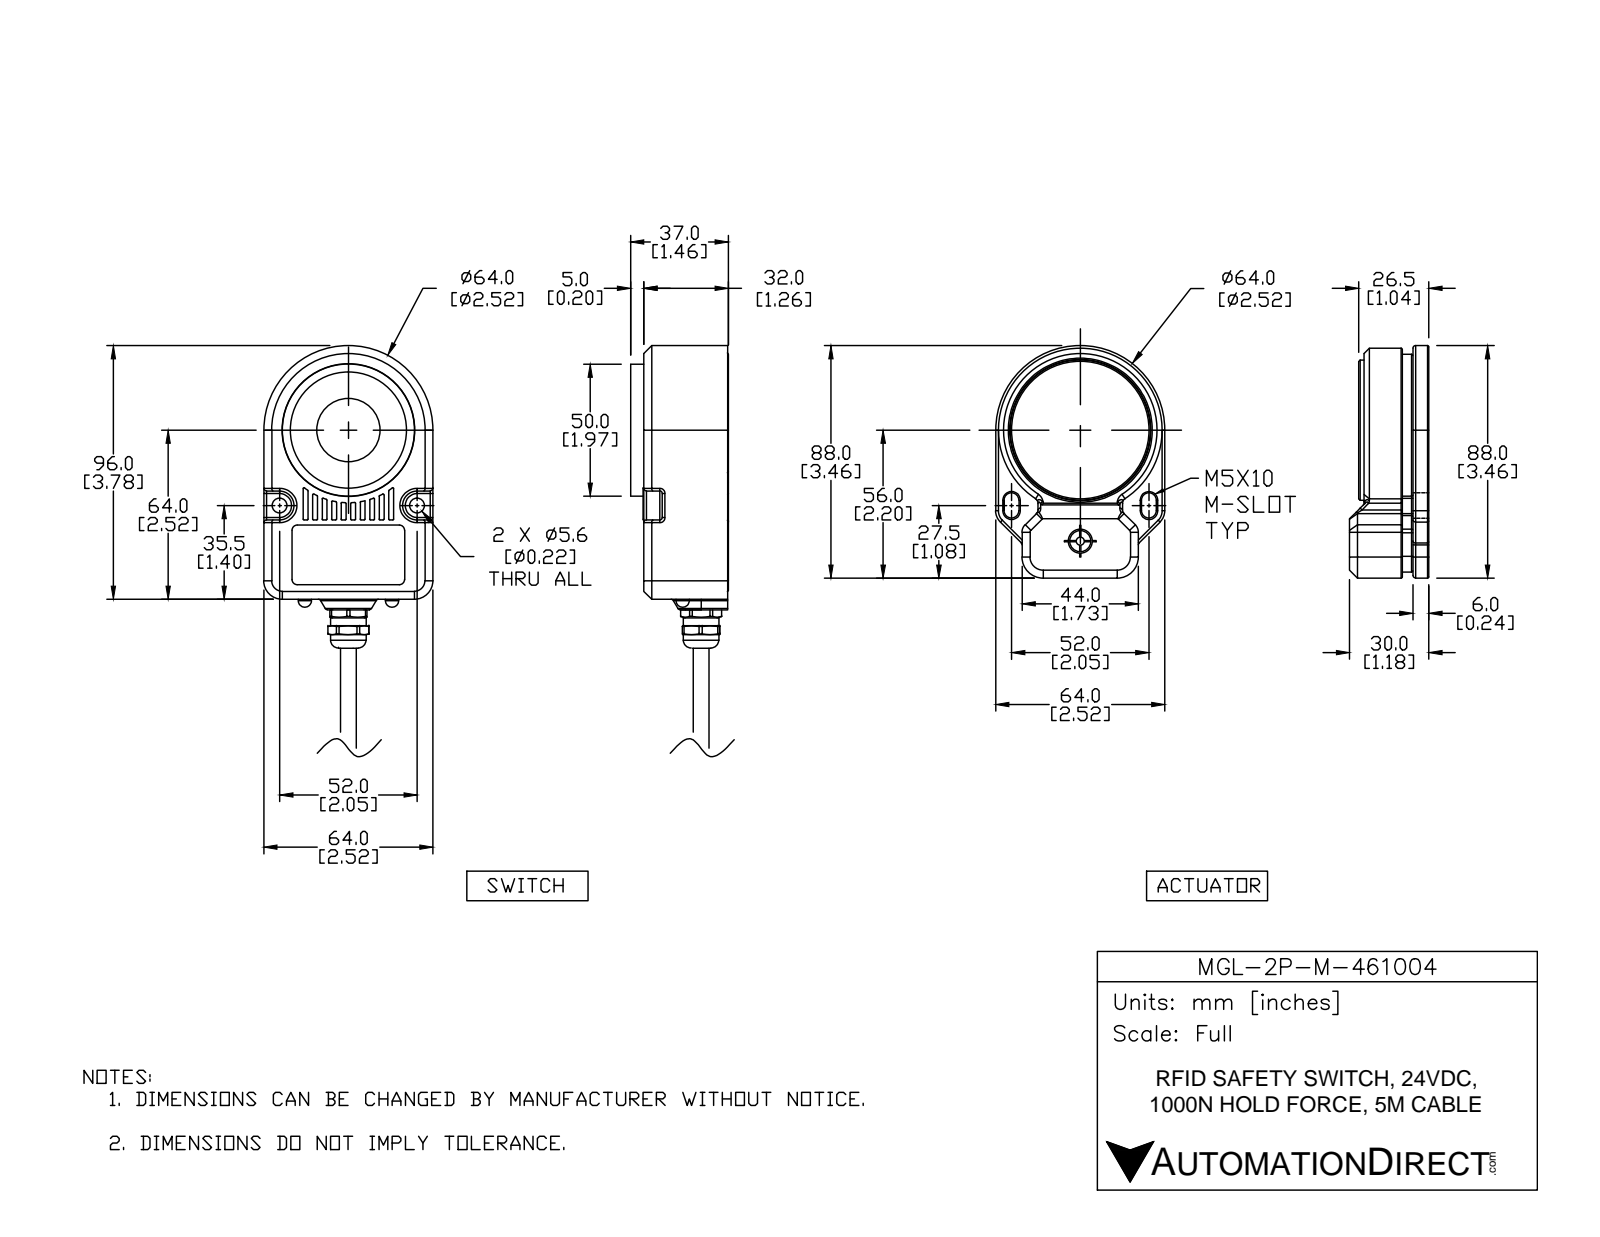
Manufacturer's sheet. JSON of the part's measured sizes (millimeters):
{"part_name": "MGL-2P-M-461004_2; MGL-2P-M-461004; MGL-2P-M-461004_1", "step_written_by": "SolidWorks 2017 (AUTOMOTIVE_DESIGN)", "units": "millimeters", "bodies": {"solids": 17, "faces": 1585, "planar": 431, "cylindrical": 674, "other": 480}, "overall_size": [196, 64.5, 64], "volume_mm3": 194400, "surface_area_mm2": 99680, "round_holes": [[4, 6], [8, 6], [2.4, 4], [5, 4], [2, 2], [3.3, 2], [5.6, 2], [9, 2], [10.5, 2], [17, 2], [6.4, 1], [6.5, 1]], "round_bosses_or_shafts": [[0.5, 4], [2, 3], [12, 2], [6, 2], [5.8, 2], [5.4, 2], [3.7, 2], [62, 1]], "partial_cylinders_radius": [[0.5, 180], [1, 60], [0.3, 39], [2, 20], [0.6, 7], [4, 6], [6, 5], [8, 5]], "face_to_face_distances": [2.5, 6, 58.5, 10.5, 16.5, 64.5, 3, 61.5, 10, 8], "hole_center_spacings": [17.9, 19.5, 27.6, 17, 26, 29.4, 4.4, 8.8]}
